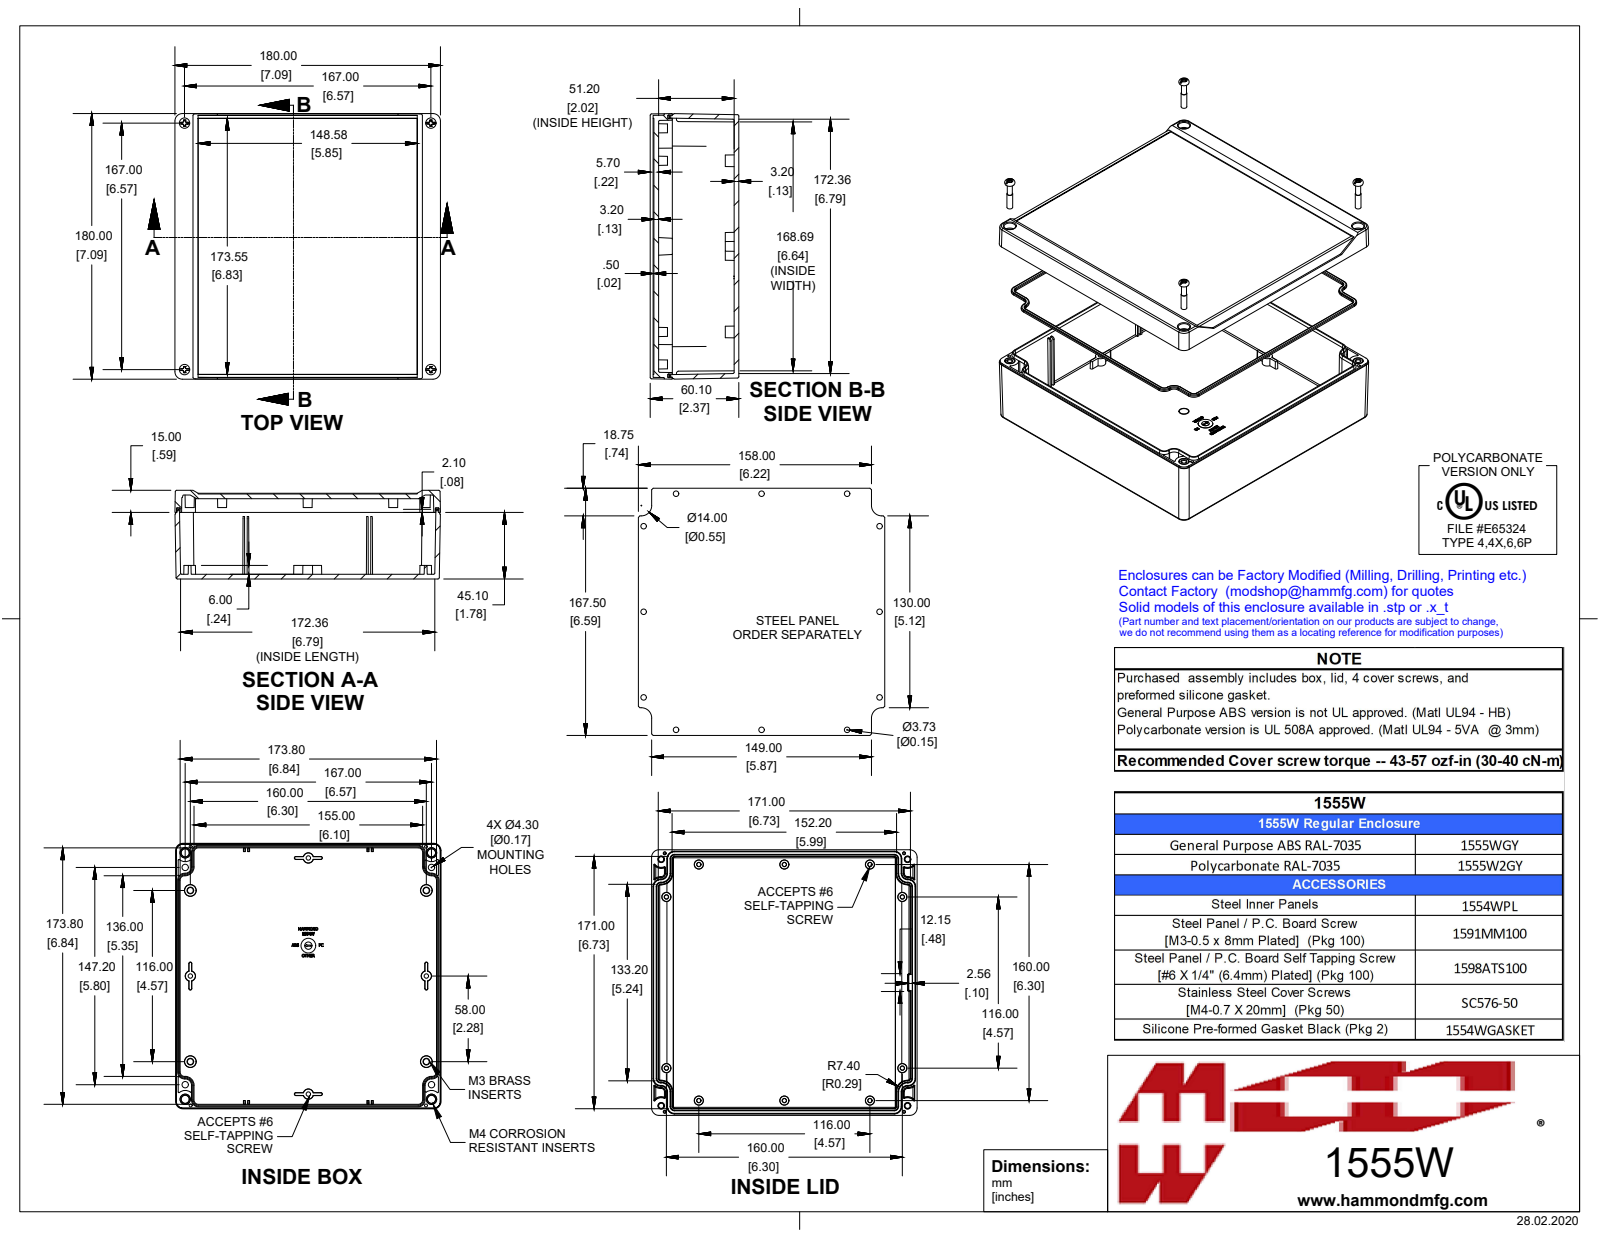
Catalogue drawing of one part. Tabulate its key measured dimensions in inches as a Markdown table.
| quantity | value |
| --- | --- |
| part name | 1555W2GY |
| STEP written by | SolidWorks 2019 (AUTOMOTIVE_DESIGN) |
| units | inches |
| bodies | 15 solids, 1940 faces (661 planar, 381 cylindrical, 898 other) |
| overall size | 7.087 × 7.087 × 2.366 |
| volume | 21.18 in³ |
| surface area | 366.9 in² |
| round holes (diameter × count) | 0.097 × 4, 0.128 × 4, 0.181 × 4, 0.138 × 3 |
| round bosses / shafts (diameter × count) | 0.25 × 4, 0.218 × 4, 0.21 × 4, 0.19 × 4, 0.154 × 4, 0.153 × 4, 0.15 × 4, 0.135 × 4 |
| partial cylindrical surfaces (radius × count) | 0.02 × 26, 0.012 × 22, 0.039 × 12, 0.031 × 10, 0.104 × 8, 0.197 × 8, 0.199 × 8, 0.118 × 4 |
| main face-to-face distances | 0.126, 2.142, 2.268, 2.016, 0.122, 7.087, 6.965, 6.909, 0.098, 0.177 |
| hole center spacings | 1.013, 5.572, 6.515, 6.575, 8.513, 4.567, 6.299, 7.781 |
